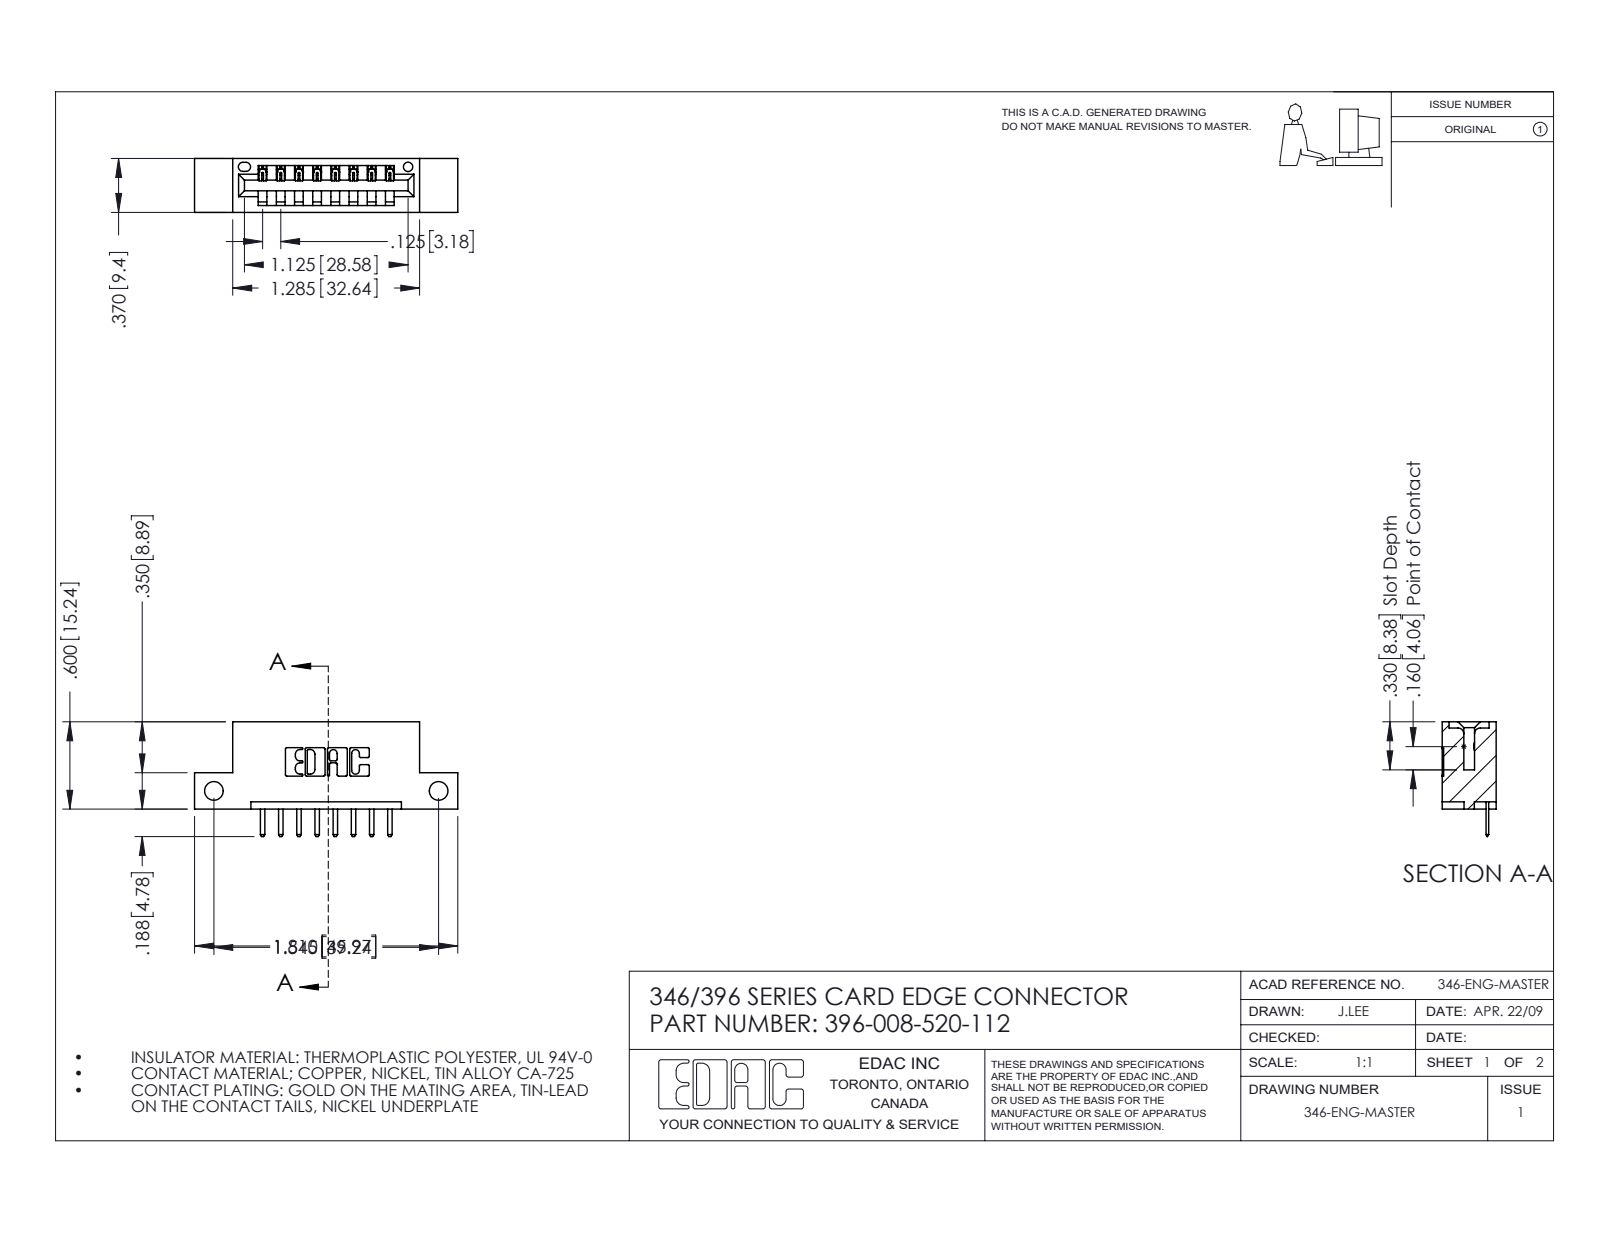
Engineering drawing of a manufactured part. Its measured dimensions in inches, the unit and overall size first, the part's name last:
Units: inches
Overall size (bounding box): 1.81 × 0.788 × 0.37
Round holes (diameter × count): ⌀0.128 ×2, ⌀0.064 ×1
Partial cylindrical surfaces — rounded edges, fillets, slot ends (radius × count): R0.01 ×22, R0.01 ×18, R0.006 ×16, R0.007 ×6, R0.031 ×6, R0.026 ×3, R0.031 ×2, R0.04 ×2
Main face-to-face distances: 0.25, 0.37, 0.048, 0.322, 0.5, 0.148, 0.222, 0.1, 0.174, 0.125
Hole centre spacings: 1.545
Volume: 0.248 in³ · Surface area: 6.944 in²
Bodies: 9 solids, 618 faces (412 planar, 206 cylindrical, 0 other)
Part name (STEP PRODUCT): 396-008-520-112; 345-292-001_345-293-120; 346 Part_Flush Mounting Lugs - Side Mount
STEP written by: SolidWorks 2016 (CONFIG_CONTROL_DESIGN)
